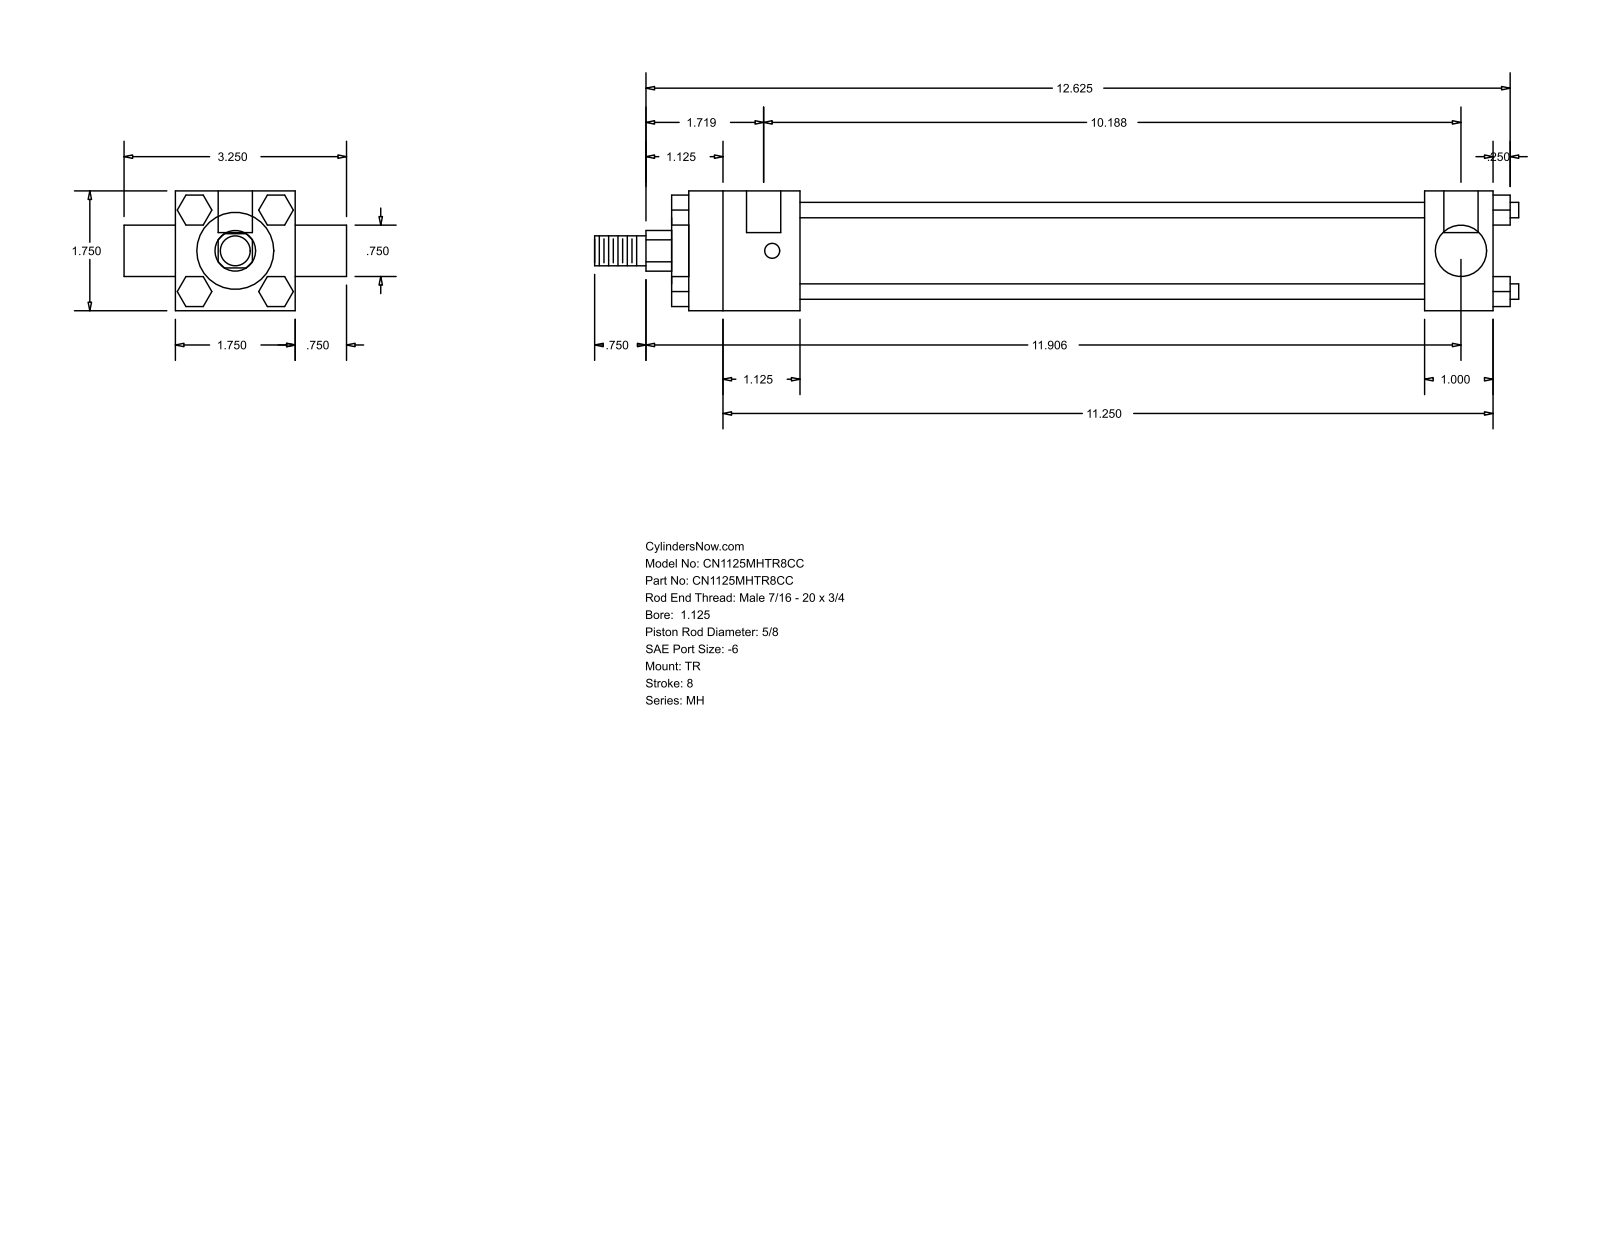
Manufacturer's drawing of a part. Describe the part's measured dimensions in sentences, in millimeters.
The part is named "MH_TR__0112_0.625". Its 3-D file was written by "GSSL Pune (CONFIG_CONTROL_DESIGN)". It is 0 solids with 120 faces: 92 planar, 28 cylindrical and 0 other. Overall it measures 342.9 by 82.55 by 44.45 millimeters. Round holes: 3 of diameter 5.56, 2 of diameter 12.7. Round bosses or shafts: 4 of diameter 5.71, 1 of diameter 34.92, 1 of diameter 28.57, 1 of diameter 19.05, 1 of diameter 15.88, 1 of diameter 11.11. Partial cylindrical surfaces (rounded edges, fillets, slot ends): 1 of radius 7.54. The main face-to-face distances are 44.46, 11.11, 231.78, 257.17, 25.39, 41.27, 273.05, 298.44, 47.62, 6.35. The hole center spacings are 3.17, 255.59, 258.76.
